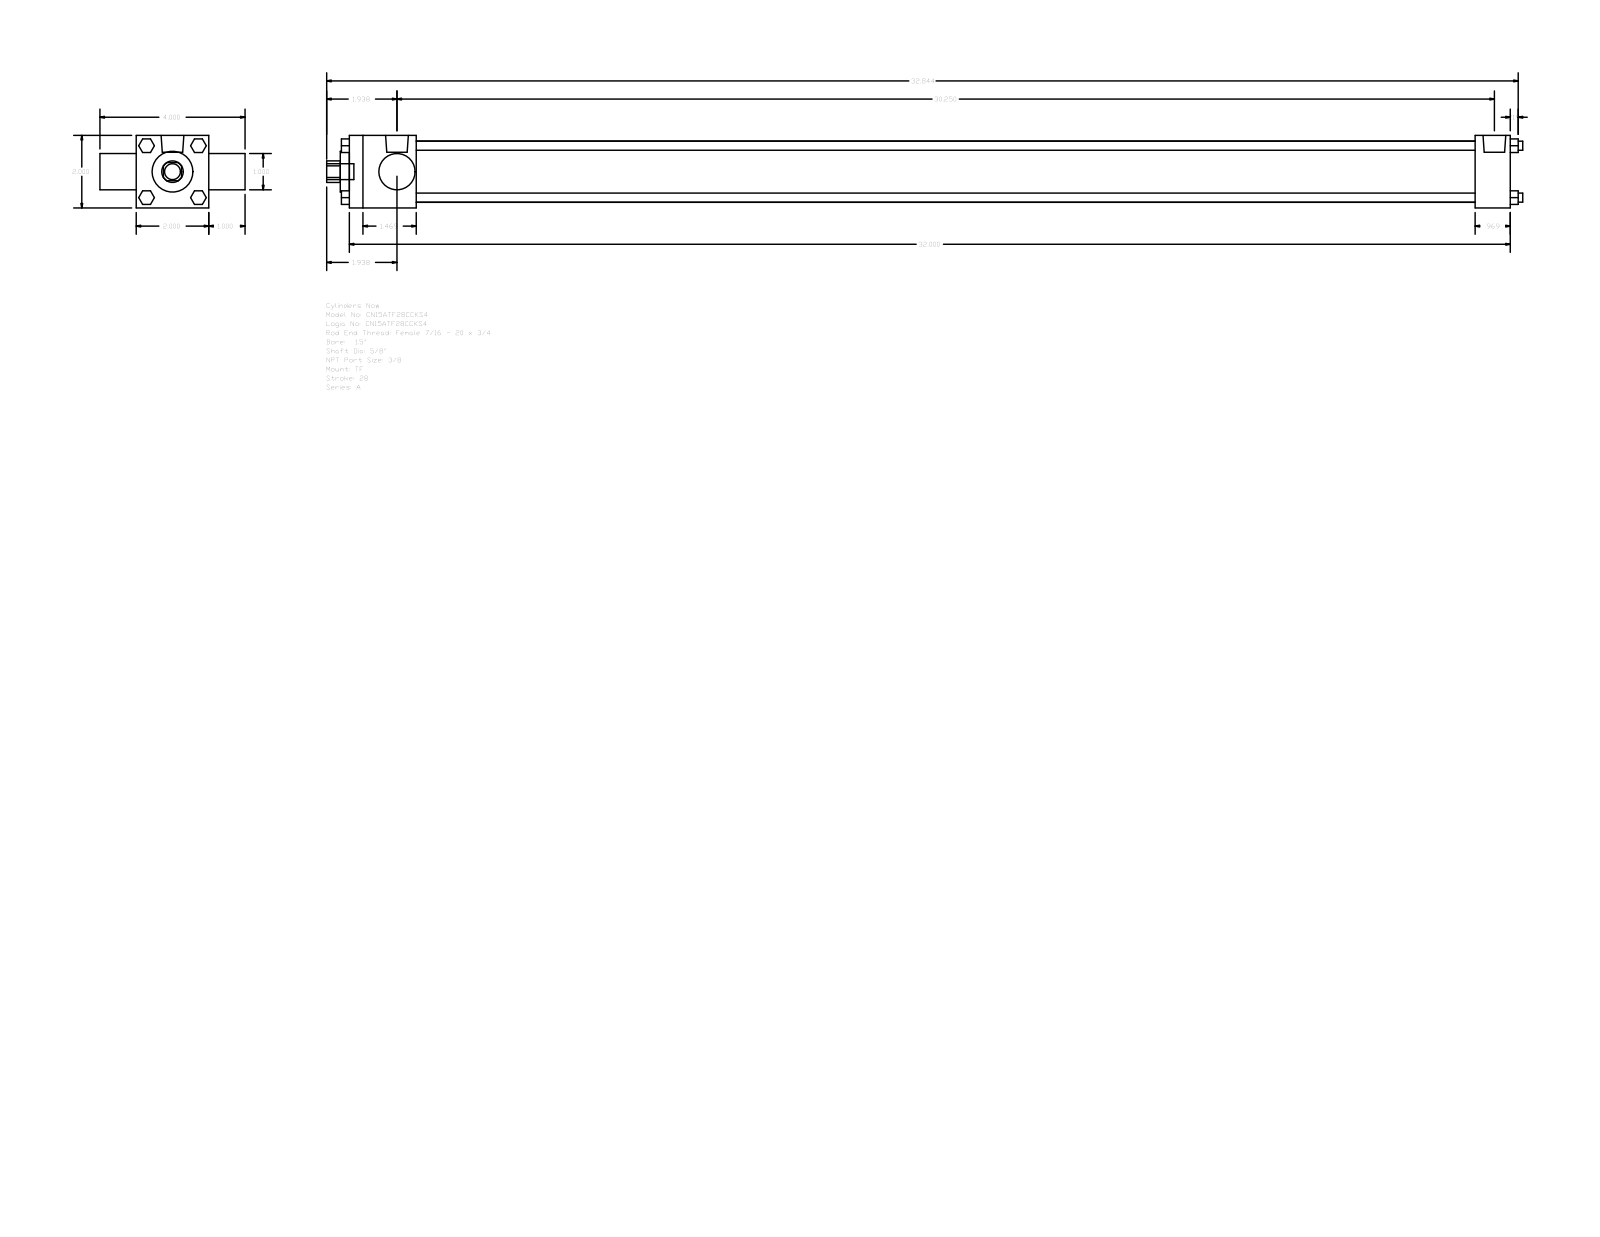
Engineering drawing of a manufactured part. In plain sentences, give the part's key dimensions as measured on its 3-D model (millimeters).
The part is named "A_TF__0150_0.625". Its 3-D file was written by "GSSL Pune (CONFIG_CONTROL_DESIGN)". It is 0 solids with 120 faces: 92 planar, 28 cylindrical and 0 other. Overall it measures 837.41 by 101.6 by 50.8 millimeters. Round holes: 1 of diameter 15.88, 1 of diameter 25.4, 1 of diameter 28.57, 1 of diameter 42.93. Round bosses or shafts: 4 of diameter 6.35, 3 of diameter 5.56, 2 of diameter 15.93, 1 of diameter 11.11. Partial cylindrical surfaces (rounded edges, fillets, slot ends): 1 of radius 7.54. The main face-to-face distances are 50.8, 812.79, 25.4, 76.2, 46.83, 788.19, 741.36, 765.96, 24.6, 9.52.
